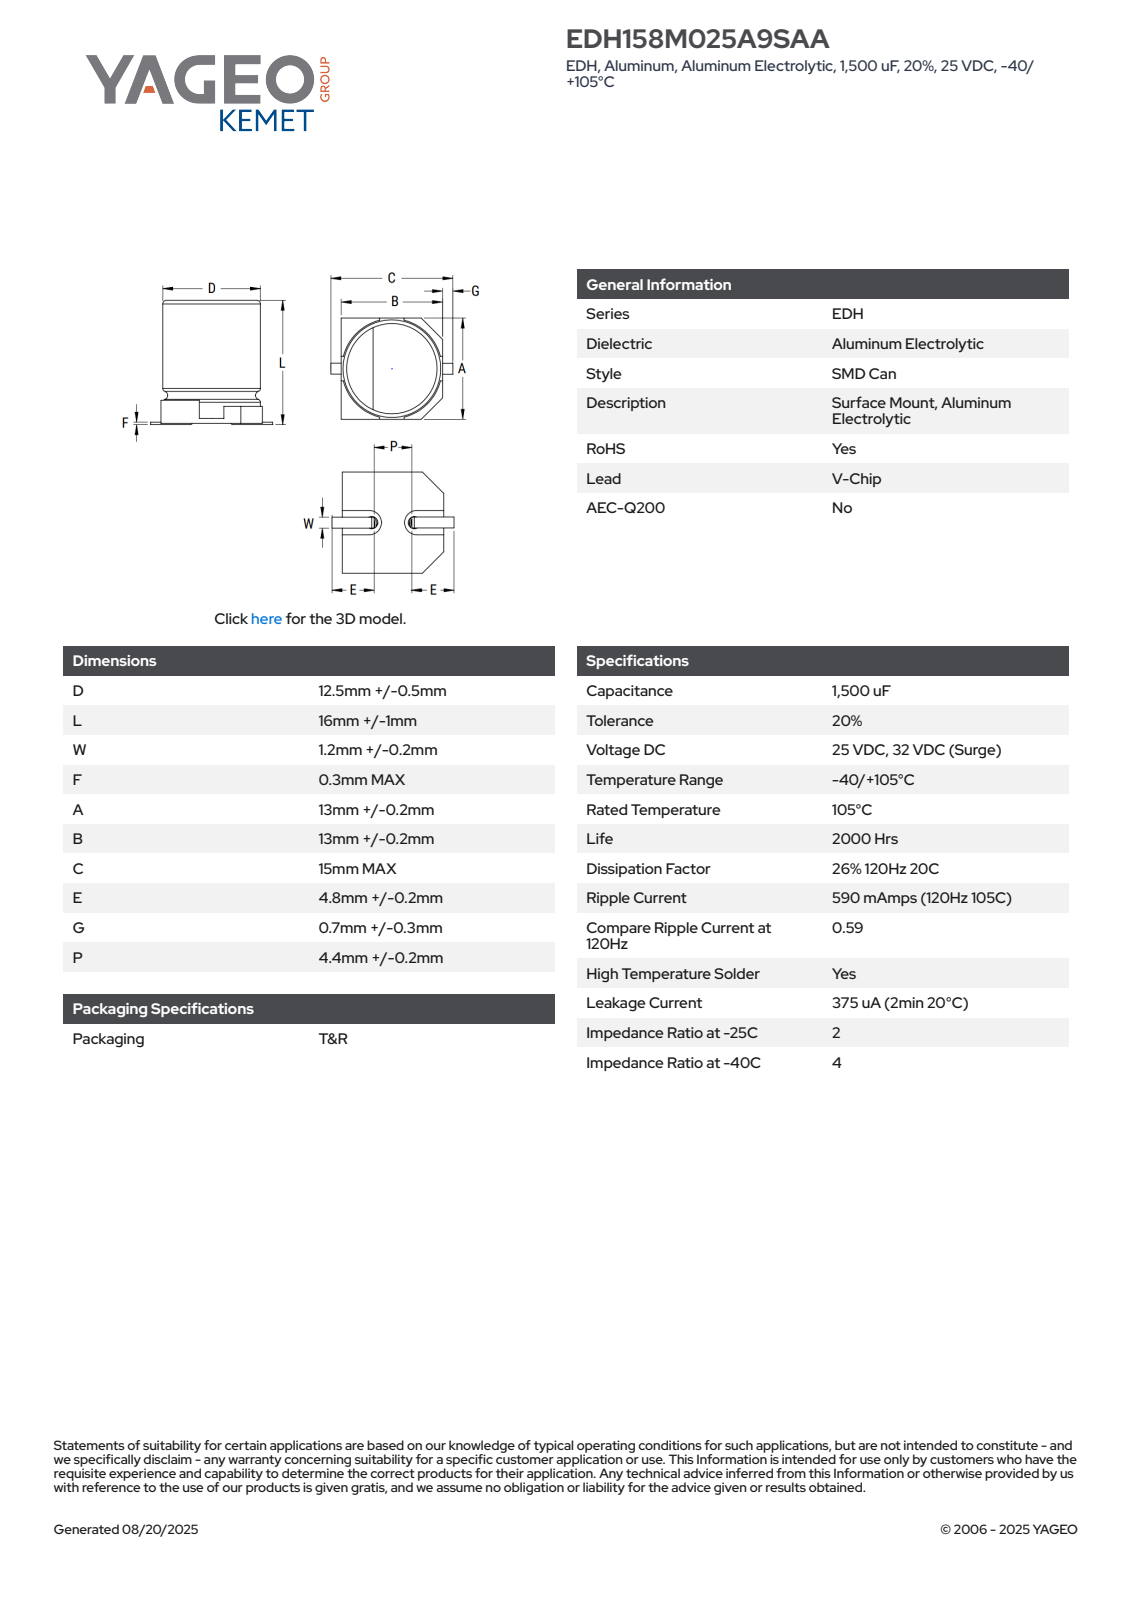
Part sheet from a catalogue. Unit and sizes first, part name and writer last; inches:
Units: inches
Overall size (bounding box): 0.669 × 0.575 × 0.52
Round bosses / shafts (diameter × count): ⌀0.489 ×1
Partial cylindrical surfaces — rounded edges, fillets, slot ends (radius × count): R0.008 ×2, R0.203 ×1, R0.256 ×1
Main face-to-face distances: 0.033, 0.657, 0.624, 0.658, 0.624, 0.52, 0.134, 0.167, 0.49, 0.491
Volume: 0.129 in³ · Surface area: 2.248 in²
Bodies: 5 solids, 78 faces (61 planar, 11 cylindrical, 6 other)
Part name (STEP PRODUCT): CAC_S_12.5X16_D13L16.5W1.45F0.3A13B13C15.2E5.1P4.8
STEP written by: SolidWorks 2021 (AUTOMOTIVE_DESIGN)
